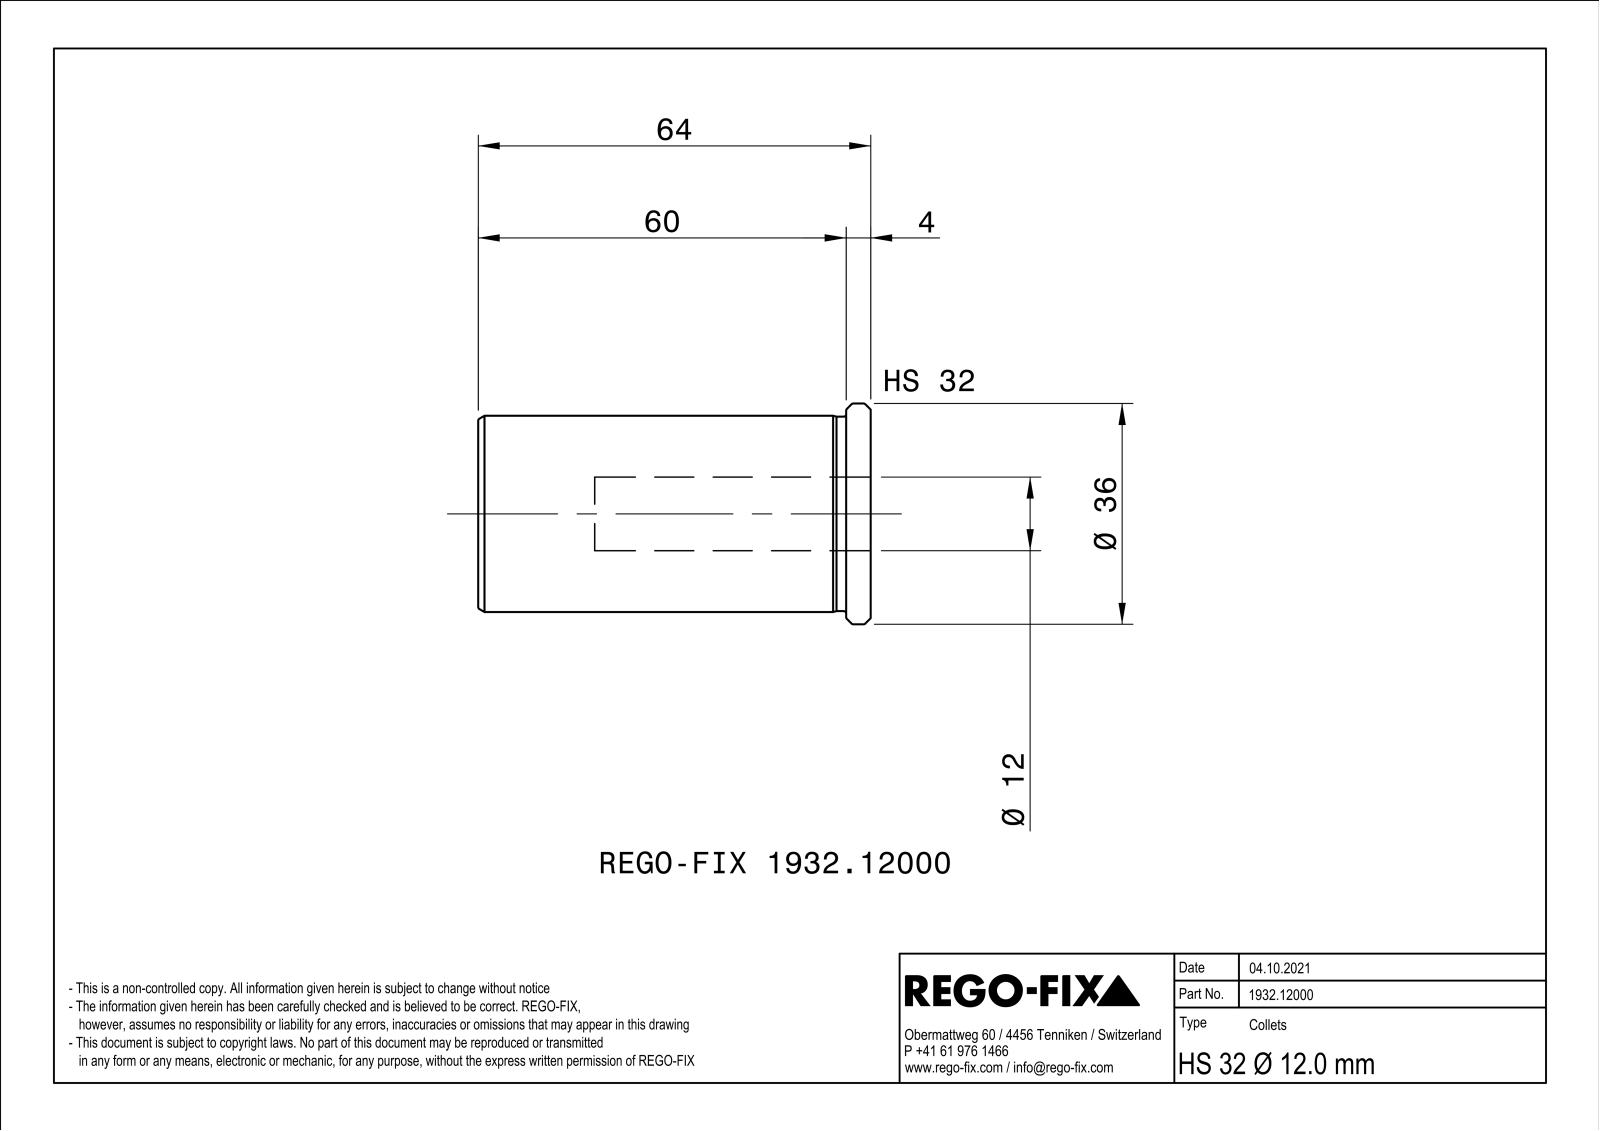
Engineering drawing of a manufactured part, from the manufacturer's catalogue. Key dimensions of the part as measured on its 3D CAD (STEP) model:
Part name (STEP PRODUCT): NOCUT
STEP written by: SIEMENS PLM Software Solid Edge ST10 (AUTOMOTIVE_DESIGN)
Units: millimetres
Bodies: 1 solid, 71 faces (22 planar, 11 cylindrical, 38 other)
Overall size (bounding box): 64 × 35.99 × 35.99
Volume: 36 625 mm³ · Surface area: 13 981 mm²
Round holes (diameter × count): ⌀12 ×1, ⌀26.5 ×1
Round bosses / shafts (diameter × count): ⌀36 ×1, ⌀32 ×1, ⌀31.7 ×1
Main face-to-face distances: 1, 64, 4, 60
